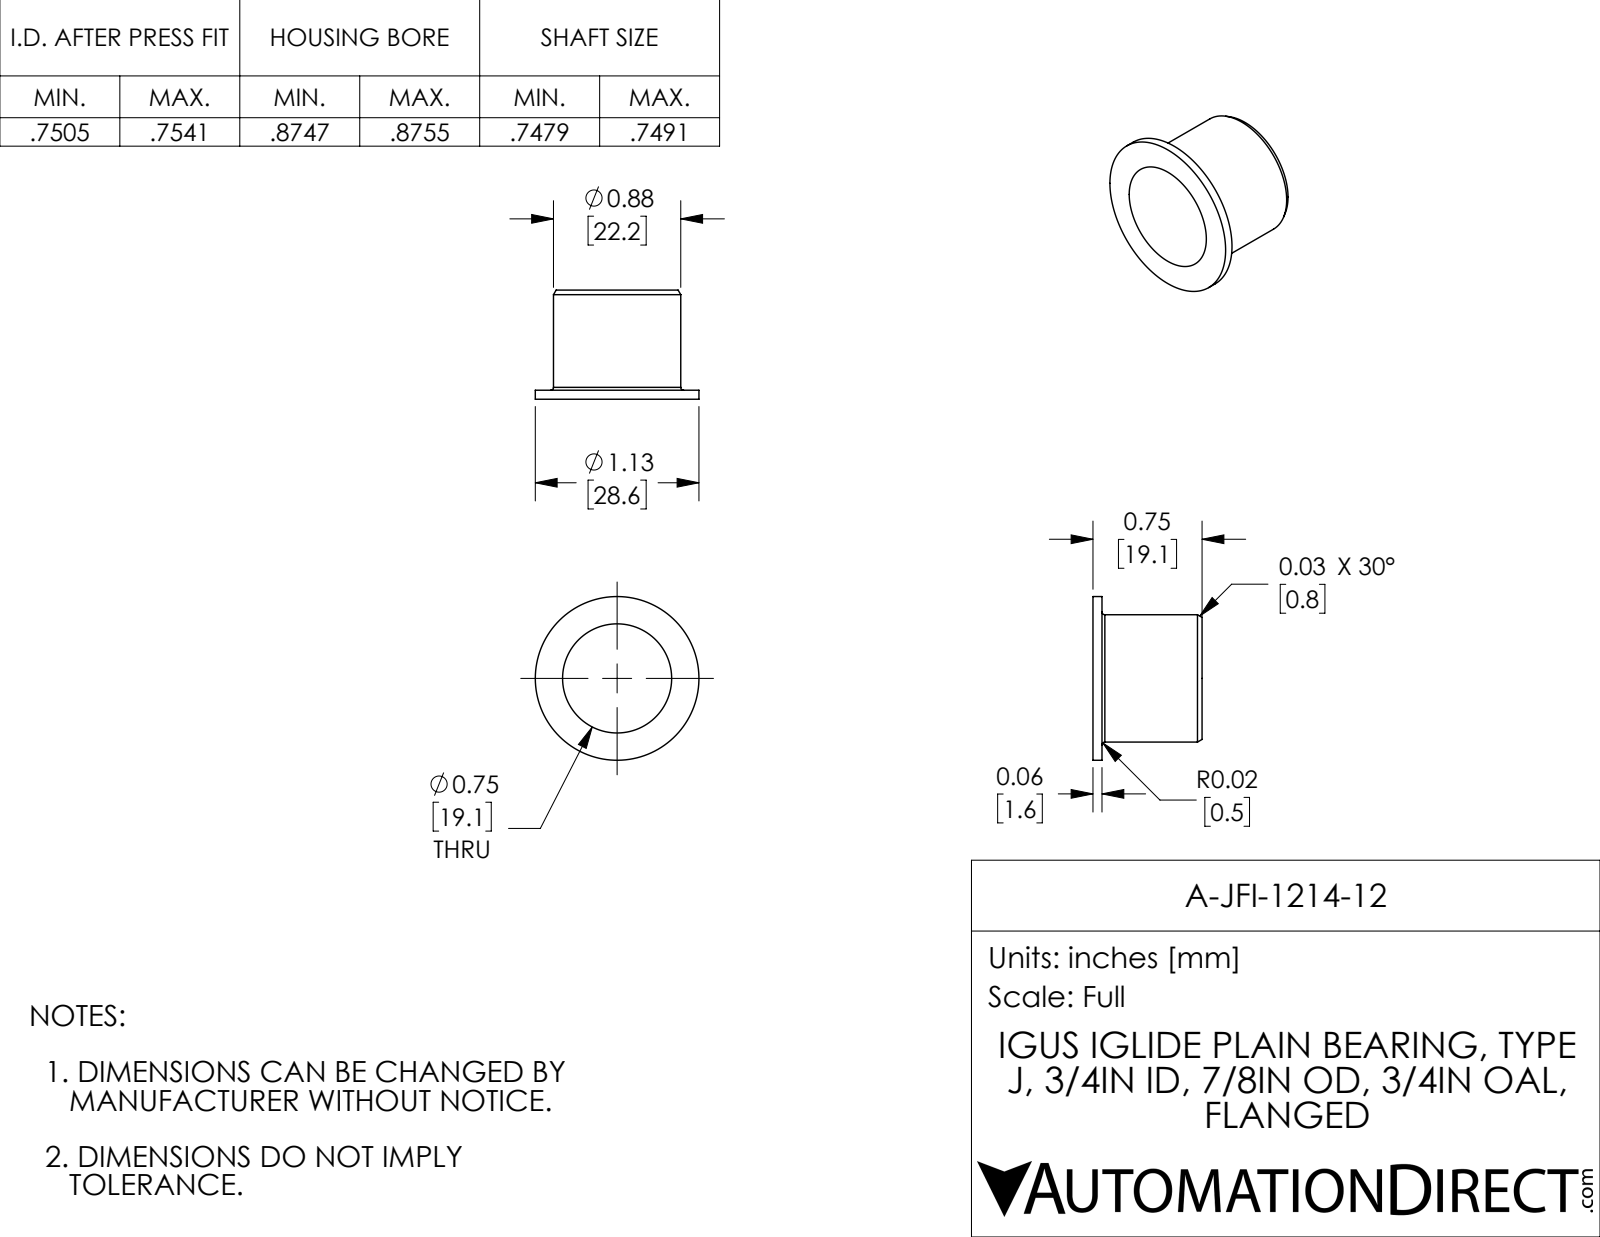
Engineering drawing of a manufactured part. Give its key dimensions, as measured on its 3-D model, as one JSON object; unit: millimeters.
{"part_name": "A-JFI-1214-12", "step_written_by": "SolidWorks 2017 (AUTOMOTIVE_DESIGN)", "units": "millimeters", "bodies": {"solids": 1, "faces": 13, "planar": 3, "cylindrical": 6, "other": 4}, "overall_size": [28.6, 28.6, 19.1], "volume_mm3": 2340, "surface_area_mm2": 3175, "round_holes": [[19.1, 1]], "round_bosses_or_shafts": [[28.6, 1], [22.2, 1]], "face_to_face_distances": [1.6, 19.1, 17.5]}
